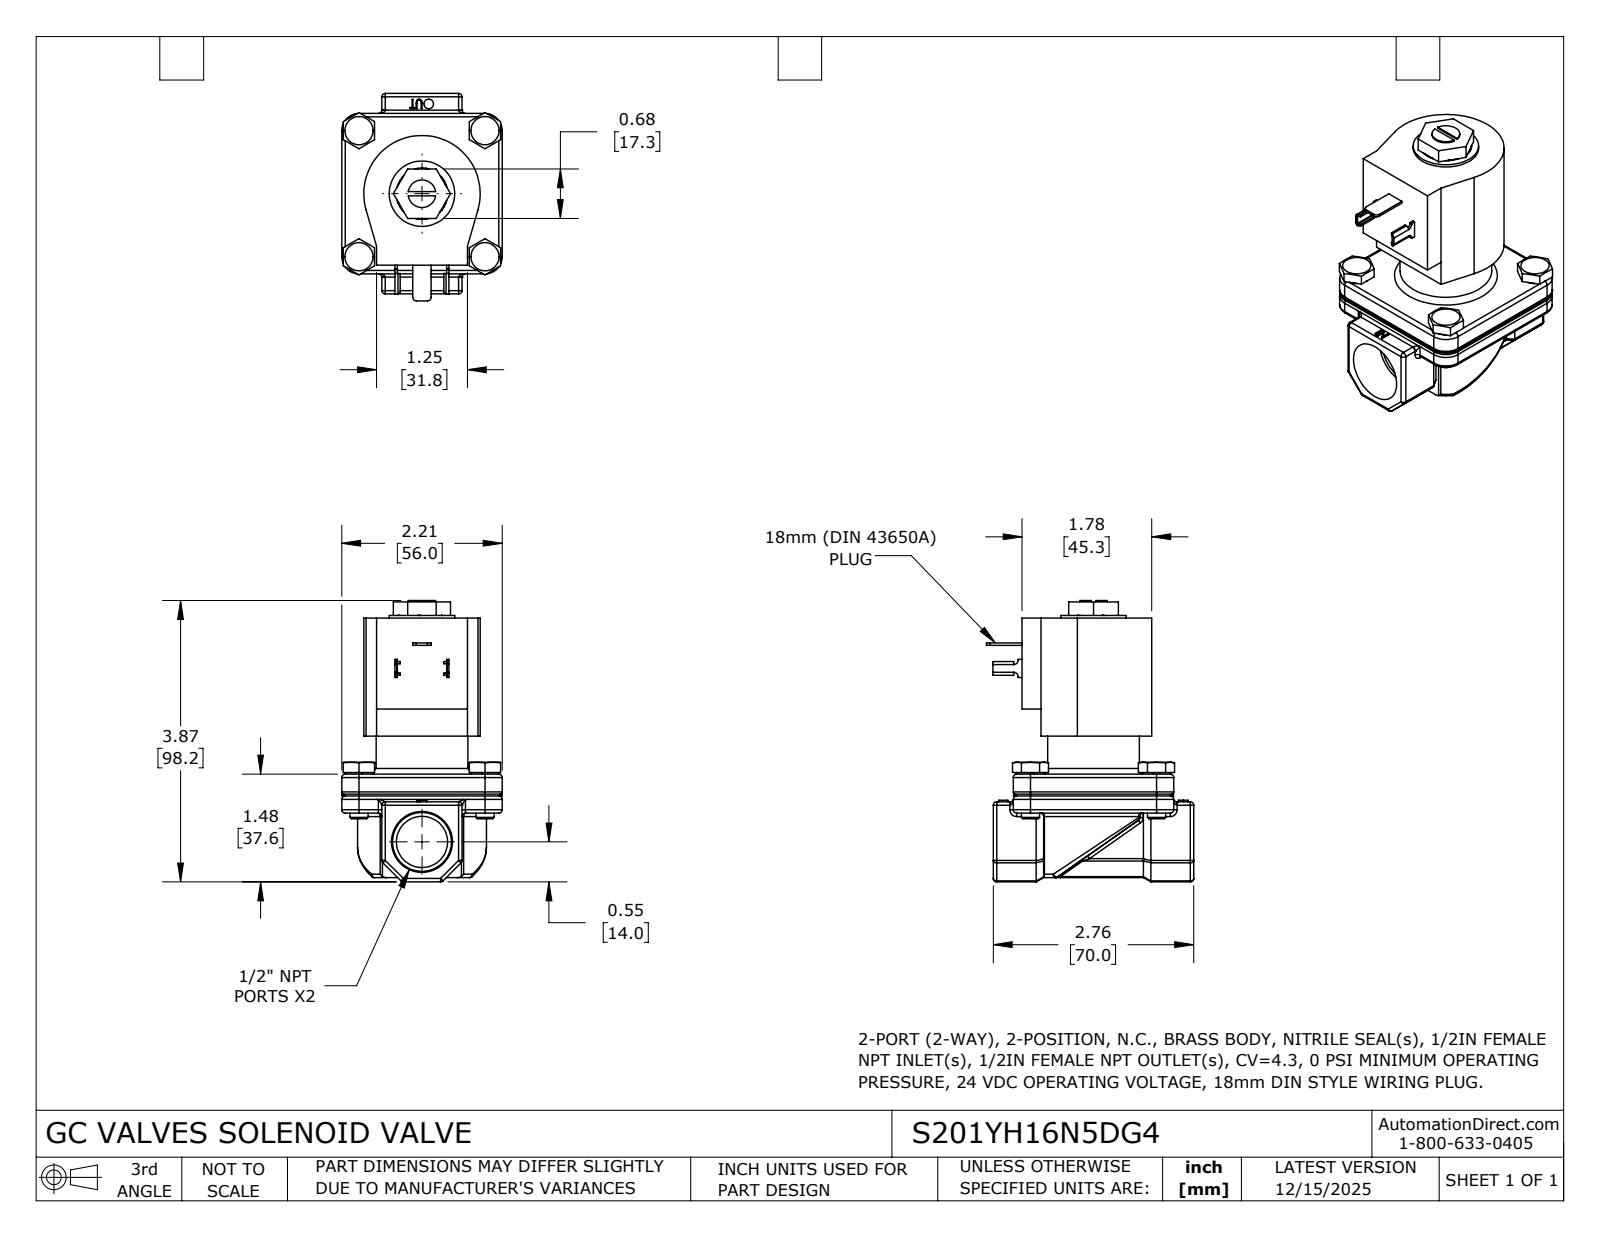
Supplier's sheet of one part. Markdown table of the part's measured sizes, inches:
| quantity | value |
| --- | --- |
| part name | S201YH16N5DG4 |
| STEP written by | SolidWorks 2024 (CONFIG_CONTROL_DESIGN) |
| units | inches |
| bodies | 1 solid, 507 faces (201 planar, 158 cylindrical, 148 other) |
| overall size | 3.867 × 2.851 × 2.205 |
| volume | 9.459 in³ |
| surface area | 42.68 in² |
| round holes (diameter × count) | 0.703 × 1, 0.706 × 1 |
| round bosses / shafts (diameter × count) | 0.388 × 4, 0.25 × 4, 1.26 × 1, 0.9 × 1, 0.464 × 1, 0.38 × 1 |
| partial cylindrical surfaces (radius × count) | 0.047 × 64, 0.006 × 4, 0.031 × 4, 0.041 × 4, 0.234 × 4, 0.236 × 4, 0.05 × 2, 0.06 × 2 |
| main face-to-face distances | 2.143, 0.059, 0.551, 1.654, 0.537, 2.68, 2.205, 0.276, 2.48, 1.06 |
